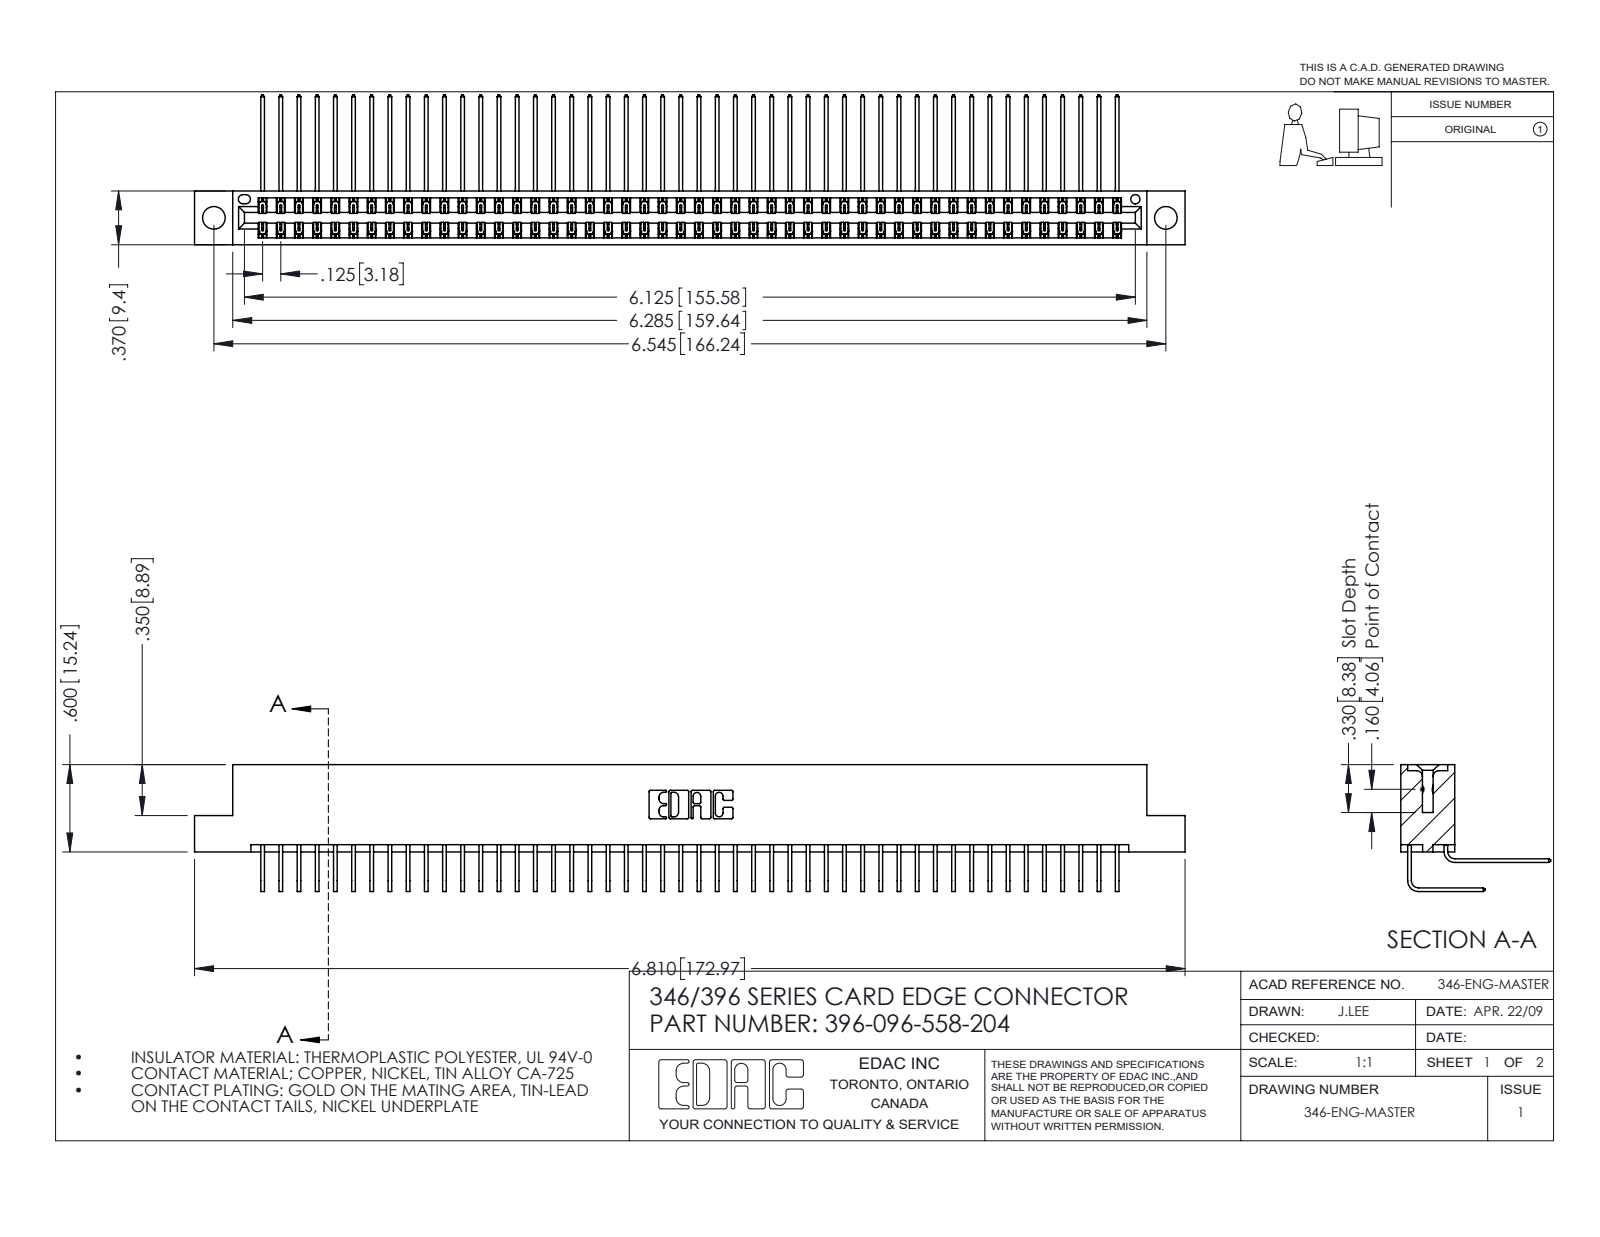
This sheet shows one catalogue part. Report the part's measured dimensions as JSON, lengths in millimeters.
{"part_name": "346 Part_Flush Mounting Lugs - 0.156 Dia-TH; 345-292-001_558 559 Tail - 1; 396-096-558-204; 345-292-001_558 Tail - 2", "step_written_by": "SolidWorks 2016 (CONFIG_CONTROL_DESIGN)", "units": "millimeters", "bodies": {"solids": 97, "faces": 5306, "planar": 3628, "cylindrical": 1678, "other": 0}, "overall_size": [173, 26.2, 22.2], "volume_mm3": 17390, "surface_area_mm2": 26450, "round_holes": [[4, 2], [1.6, 1]], "partial_cylinders_radius": [[0.2, 144], [0.3, 22], [0.2, 6], [0.8, 6], [0.7, 3], [0.4, 2], [0.6, 2], [0.6, 2]], "face_to_face_distances": [8.2, 1.2, 0.6, 9.4, 6.4, 7.6, 1.8, 7, 3.8, 5.6], "hole_center_spacings": [6.2, 160.9, 166.2]}
